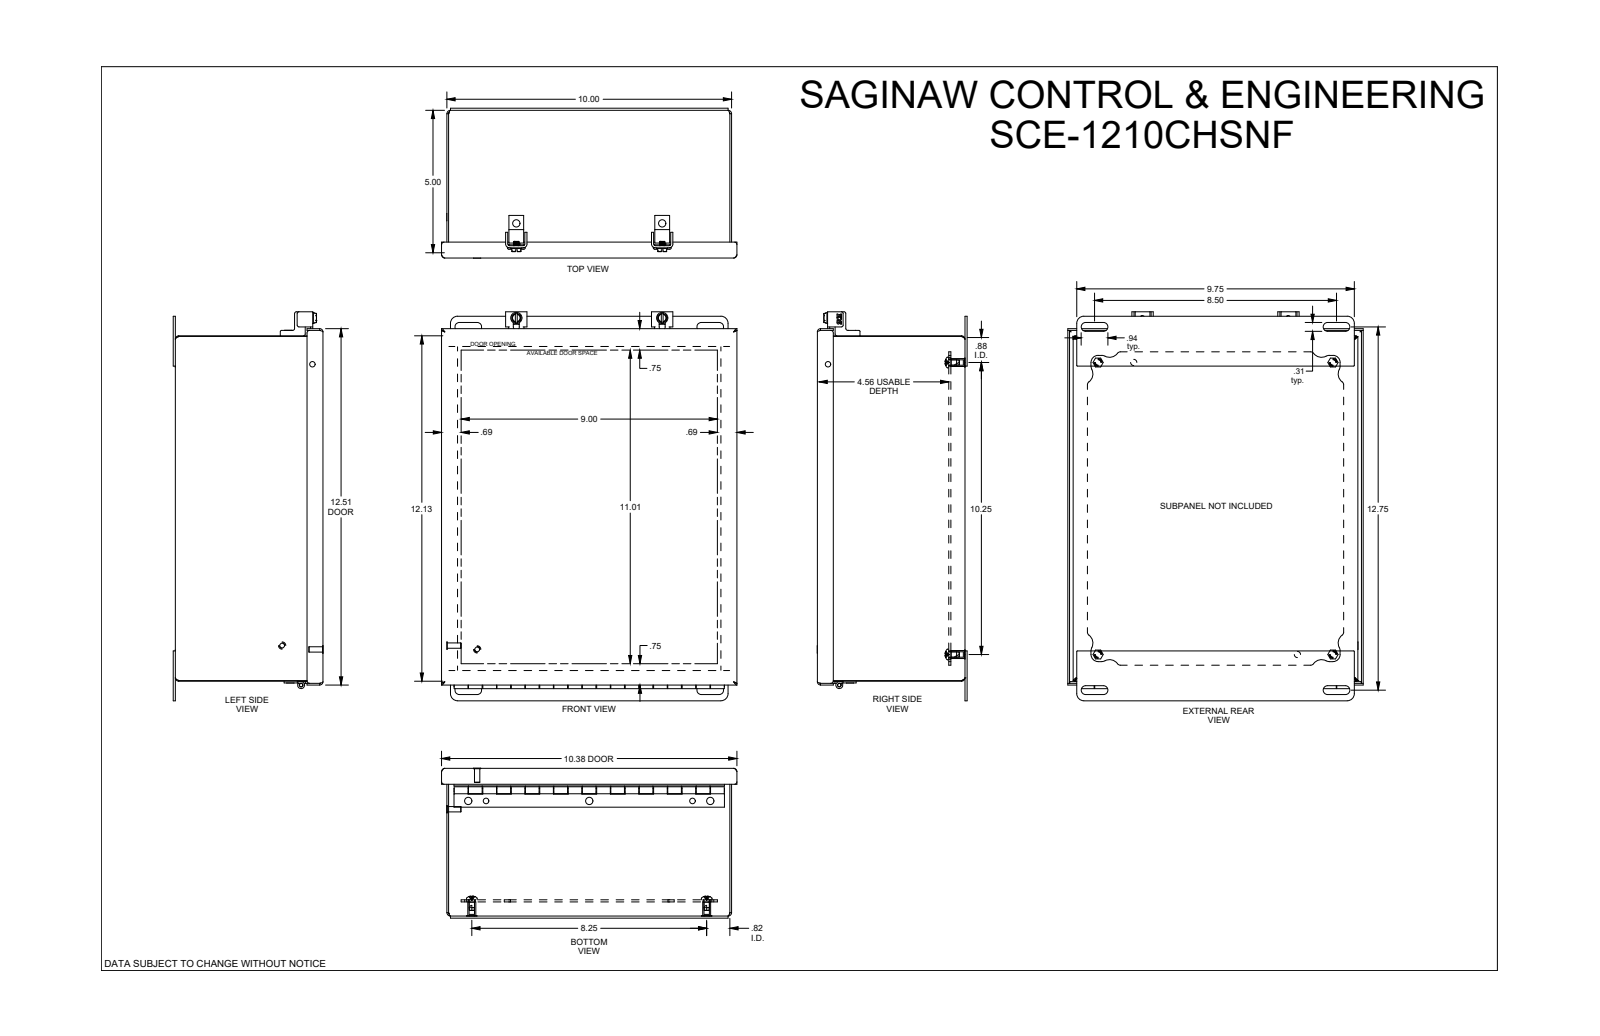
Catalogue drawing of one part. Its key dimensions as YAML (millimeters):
part_name: "SCE-1210CHSNF"
step_written_by: "SolidWorks 2019 (AUTOMOTIVE_DESIGN)"
units: millimeters
bodies: {solids: 37, faces: 1235, planar: 542, cylindrical: 346, other: 347}
overall_size: [346.9, 263.5, 133.7]
volume: 729600
surface_area: 893500
round_holes:
  - {diameter: 4.8, count: 9}
  - {diameter: 4.9, count: 7}
  - {diameter: 6.4, count: 4}
  - {diameter: 7.1, count: 4}
  - {diameter: 4, count: 2}
  - {diameter: 5.5, count: 2}
  - {diameter: 6.8, count: 2}
  - {diameter: 3.2, count: 1}
  - {diameter: 4.7, count: 1}
  - {diameter: 4.9, count: 1}
round_bosses_or_shafts:
  - {diameter: 4.8, count: 11}
  - {diameter: 6.5, count: 7}
  - {diameter: 9.5, count: 4}
  - {diameter: 7.1, count: 4}
  - {diameter: 10.1, count: 2}
  - {diameter: 4.8, count: 2}
  - {diameter: 6.2, count: 1}
  - {diameter: 3.1, count: 1}
partial_cylinders:
  - {radius: 0.3, count: 76}
  - {radius: 1.5, count: 25}
  - {radius: 1.3, count: 16}
  - {radius: 6.4, count: 16}
  - {radius: 3.2, count: 8}
  - {radius: 4, count: 8}
  - {radius: 8.7, count: 8}
  - {radius: 0.7, count: 6}
face_to_face_distances: [1.5, 130.2, 131.7, 128.7, 252.5, 1.9, 14.5, 13, 115.7, 117.2]
hole_center_spacings: [260.4, 2.3, 207.9, 262, 334.4, 262.3, 302.6, 2.3]
